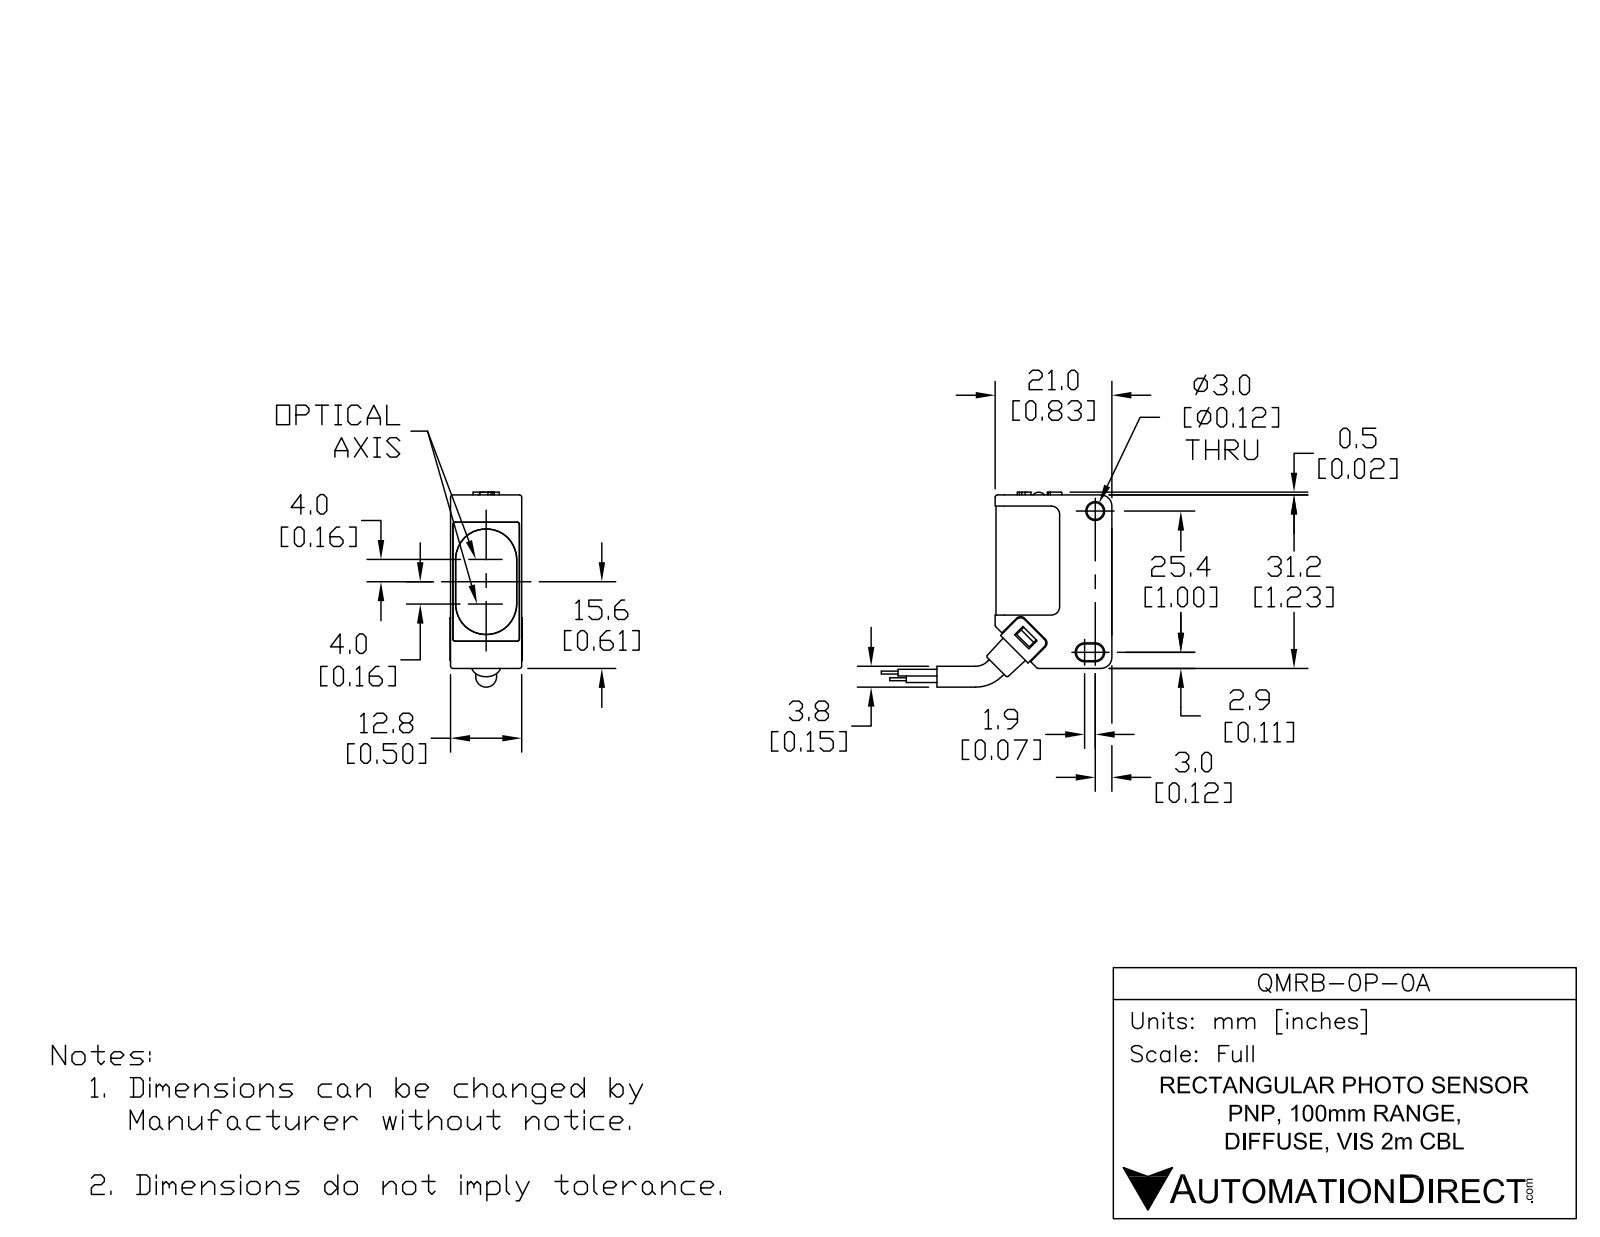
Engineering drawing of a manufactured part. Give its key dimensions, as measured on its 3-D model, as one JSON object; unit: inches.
{"part_name": "QMRB-0P-0A", "step_written_by": "SolidWorks 2017 (AUTOMOTIVE_DESIGN)", "units": "inches", "bodies": {"solids": 9, "faces": 258, "planar": 134, "cylindrical": 100, "other": 24}, "overall_size": [3.193, 1.032, 0.512], "volume_in3": 0.47, "surface_area_in2": 8.375, "round_holes": [[0.118, 3], [0.148, 1], [0.224, 1], [0.283, 1]], "round_bosses_or_shafts": [[0.138, 2]], "partial_cylinders_radius": [[0.016, 13], [0.02, 10], [0.039, 8], [0.059, 6], [0.024, 4], [0.006, 2], [0.035, 2], [0.044, 2]], "face_to_face_distances": [0.02, 0.498, 0.059, 0.016, 0.504, 0.138, 0.488, 0.079, 0.482, 0.492], "hole_center_spacings": [0.205]}
